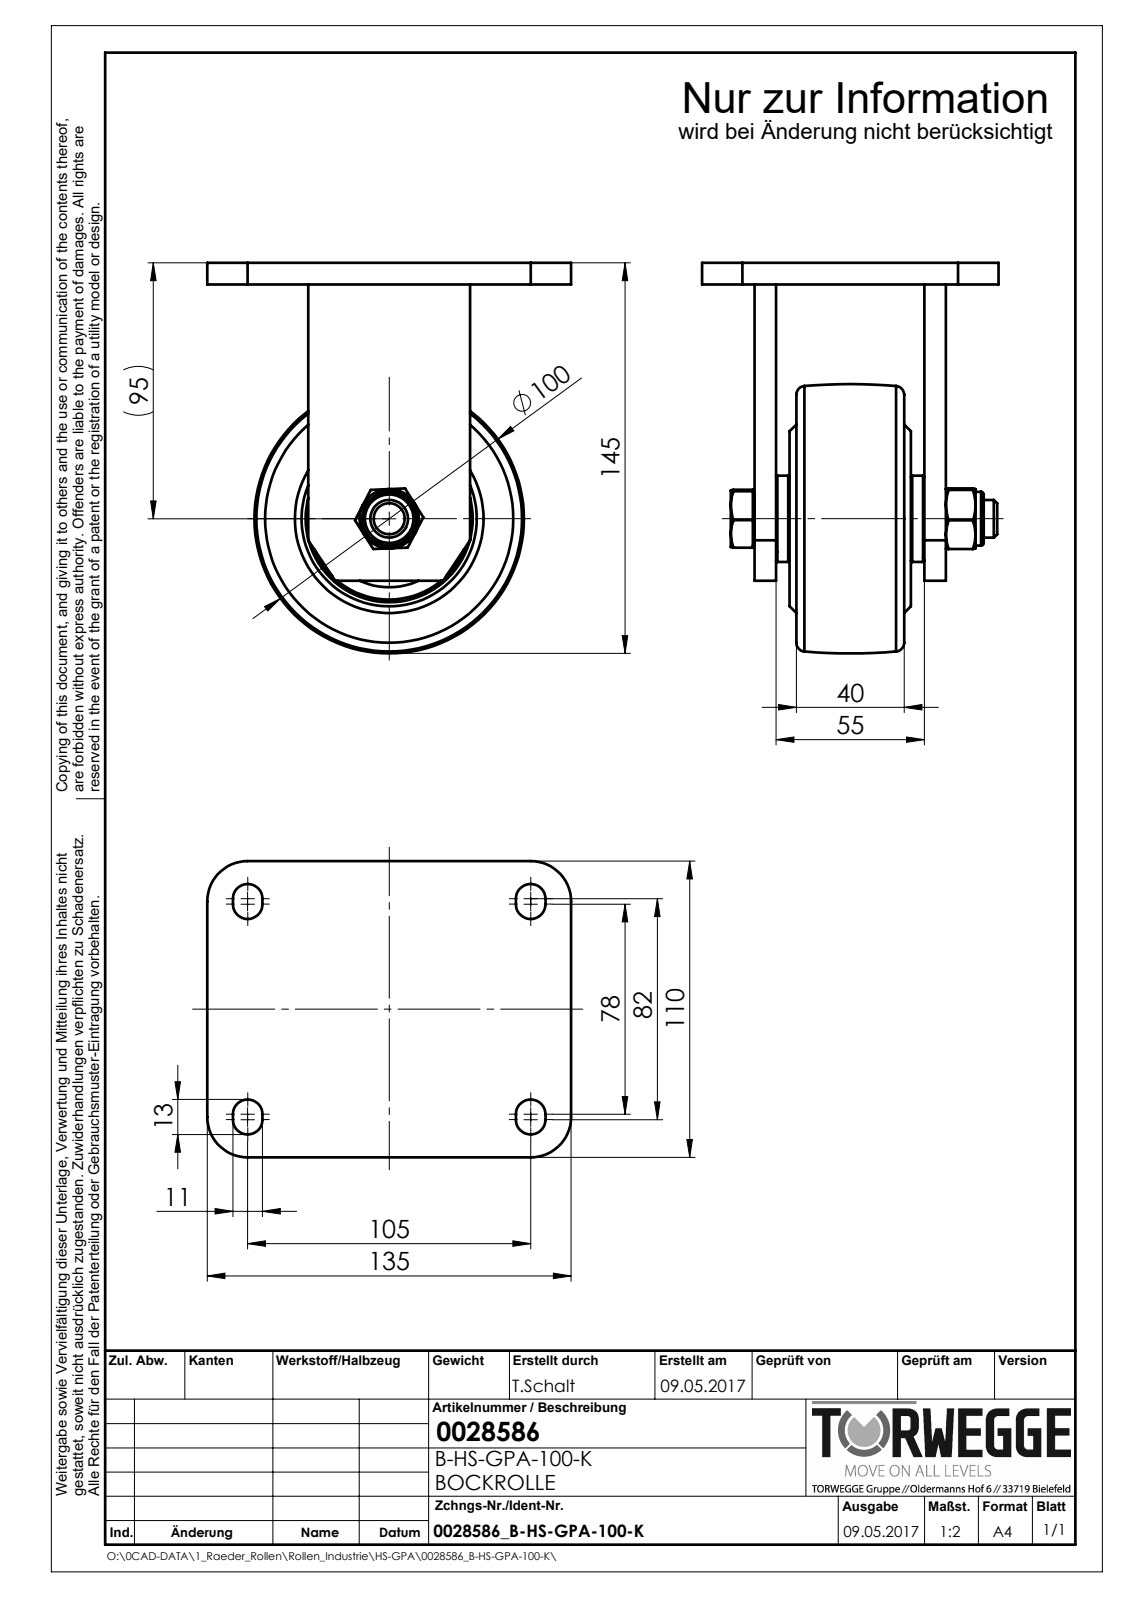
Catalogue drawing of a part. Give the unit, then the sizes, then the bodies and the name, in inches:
Units: inches
Overall size (bounding box): 5.709 × 5.315 × 4.331
Round holes (diameter × count): ⌀0.466 ×1, ⌀0.551 ×1, ⌀0.563 ×1, ⌀0.984 ×1, ⌀1.024 ×1, ⌀2.004 ×1, ⌀2.441 ×1
Round bosses / shafts (diameter × count): ⌀1.421 ×1, ⌀1.26 ×1, ⌀0.787 ×1
Partial cylindrical surfaces — rounded edges, fillets, slot ends (radius × count): R0.217 ×8, R0.591 ×4
Main face-to-face distances: 0.315, 2.48, 2.165, 2.795, 0.61, 2.185, 0.295, 1.87, 0.197, 0.512
Bodies: 0 solids, 143 faces (63 planar, 33 cylindrical, 47 other)
Part name (STEP PRODUCT): 0028586_B-HS-GPA-100-K
STEP written by: SolidWorks 2016 (CONFIG_CONTROL_DESIGN)
